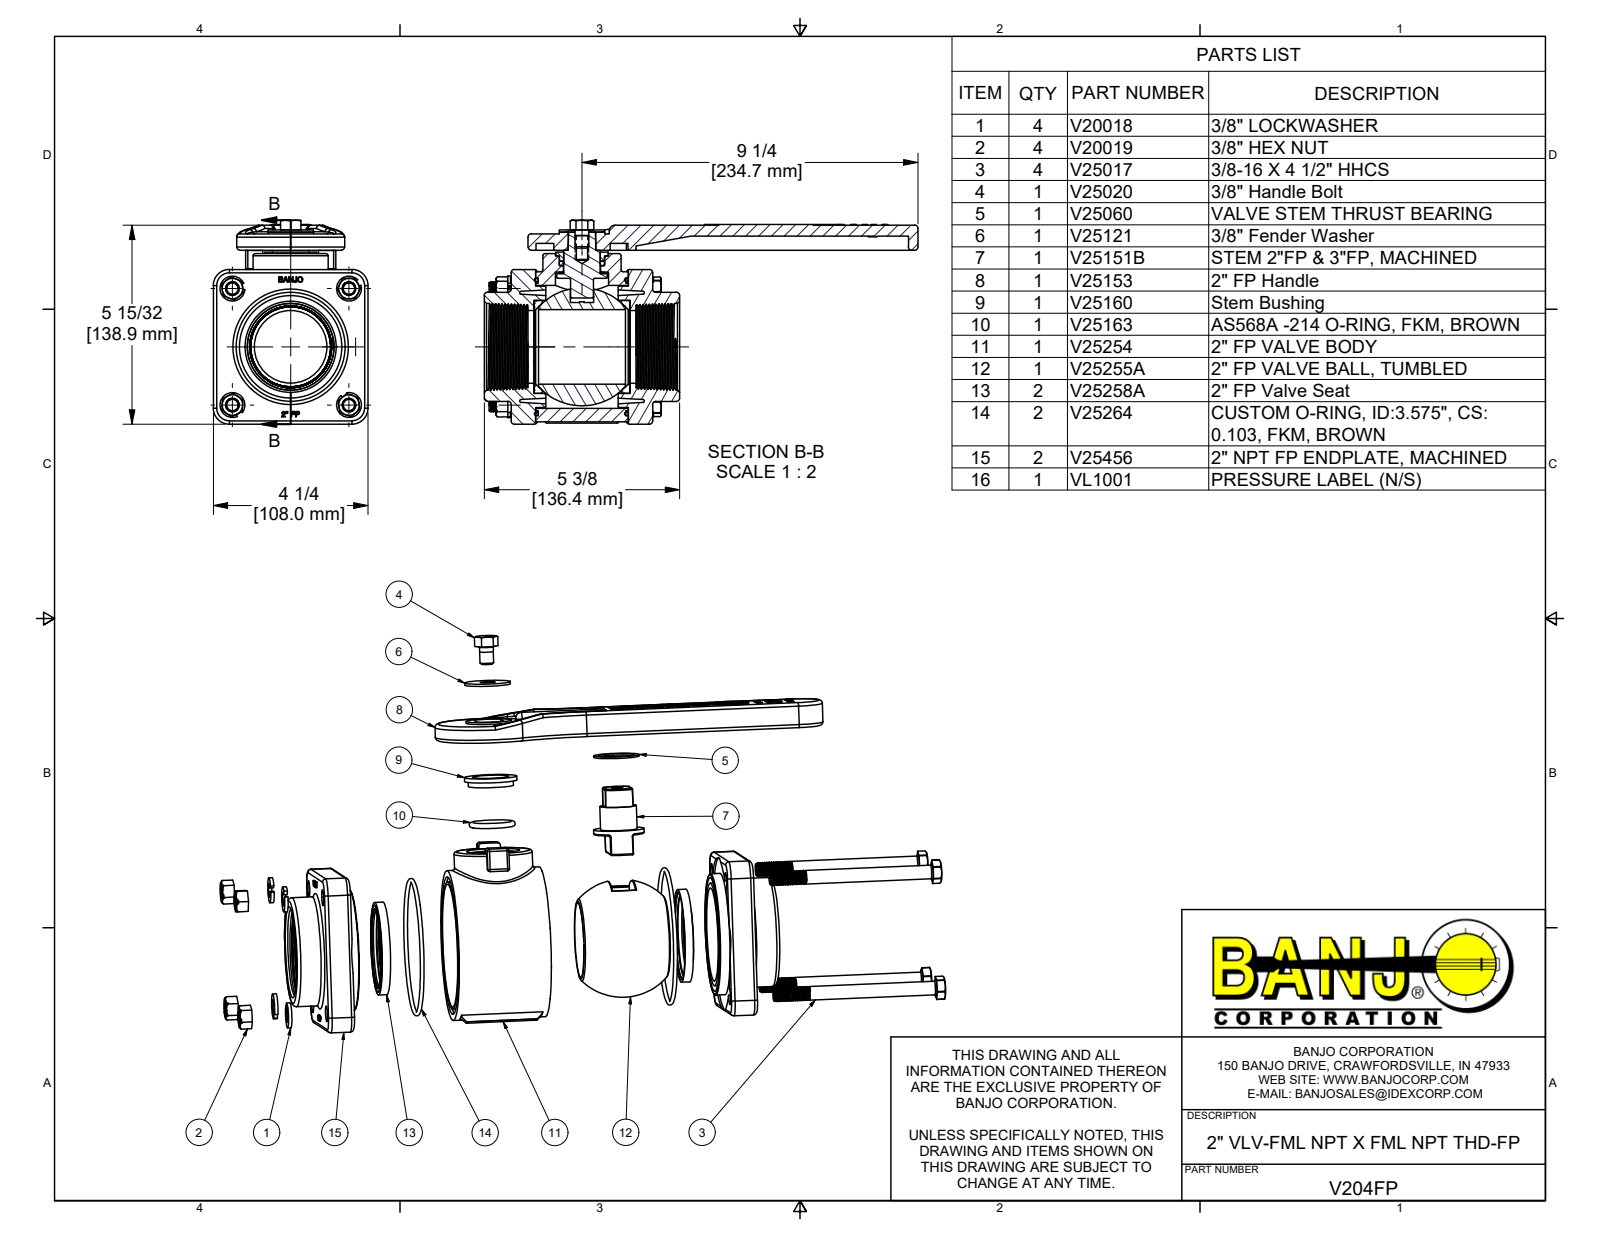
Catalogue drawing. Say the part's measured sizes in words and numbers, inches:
The part is named "V25254; VL1001; VX25356; V25456 (+8 more)". Its 3-D file was written by "Autodesk Inventor 2014 (AUTOMOTIVE_DESIGN)". It is 28 solids with 1929 faces: 831 planar, 462 cylindrical and 636 other. Overall it measures 11.925 by 5.606 by 4.25 inches. Its volume is 55.9 cubic inches and its surface area 428.5 square inches. Round holes: 12 of diameter 0.17, 4 of diameter 0.307, 4 of diameter 0.385, 4 of diameter 0.438, 1 of diameter 0.307, 1 of diameter 0.406, 1 of diameter 0.681, 1 of diameter 0.962, 1 of diameter 1, 1 of diameter 1.016, 1 of diameter 1.245, 1 of diameter 1.46. Round bosses or shafts: 60 of diameter 0.324, 5 of diameter 0.375, 4 of diameter 0.687, 1 of diameter 3.5, 1 of diameter 3.34, 1 of diameter 3, 1 of diameter 2.969, 1 of diameter 2.55. Partial cylindrical surfaces (rounded edges, fillets, slot ends): 24 of radius 0.09, 12 of radius 0.06, 10 of radius 0.032, 8 of radius 0.063, 8 of radius 0.162, 6 of radius 0.156, 4 of radius 0.03, 4 of radius 0.32. The main face-to-face distances are 0.67, 3.22, 3.89, 0.05, 0.26, 1.385, 2.865, 0.3, 4.25, 0.67. The hole center spacings are 1.977, 2.796, 3.82, 1.023, 1.133, 2.136, 3.007, 3.424.
